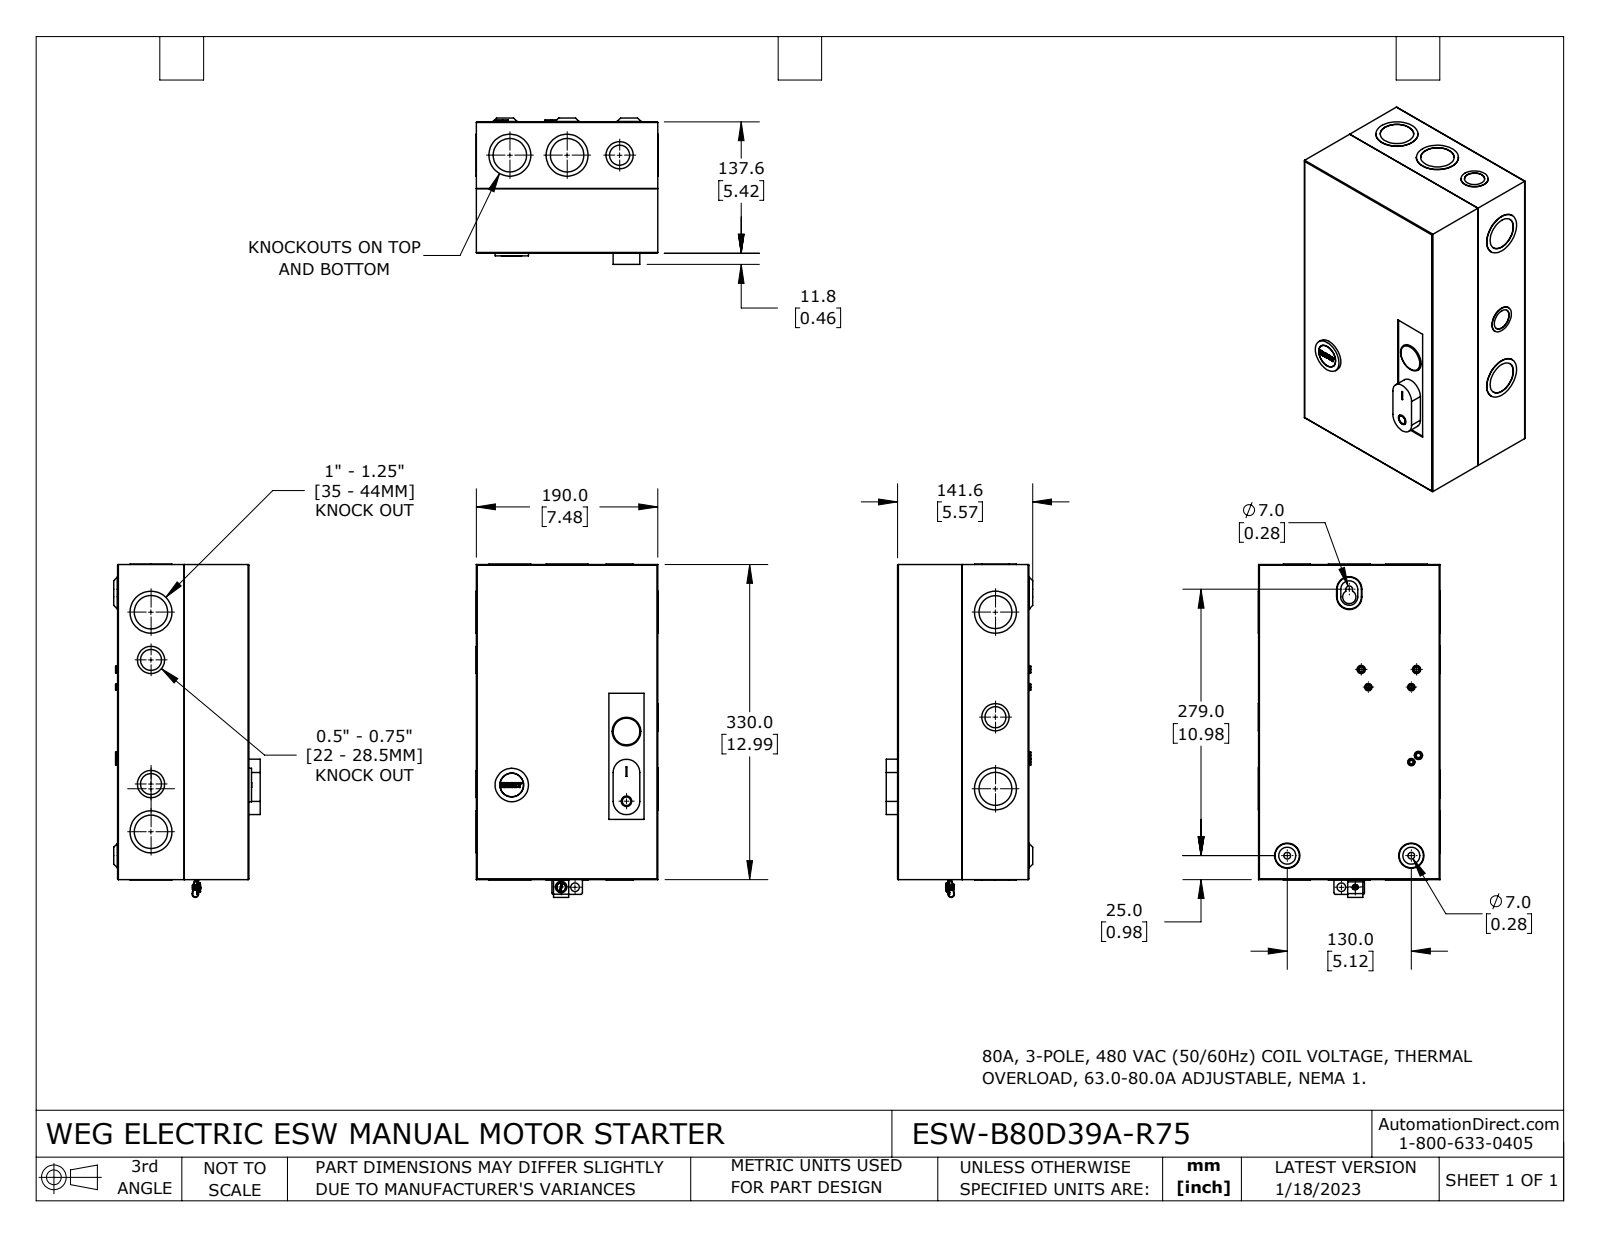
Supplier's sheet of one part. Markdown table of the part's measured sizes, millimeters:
| quantity | value |
| --- | --- |
| part name | ESW-B80D39A-R75 |
| STEP written by | SolidWorks 2021 (CONFIG_CONTROL_DESIGN) |
| units | millimeters |
| bodies | 7 solids, 435 faces (161 planar, 221 cylindrical, 53 other) |
| overall size | 349 × 190.6 × 153.4 |
| volume | 402 800 mm³ |
| surface area | 604 300 mm² |
| round holes (diameter × count) | 35 × 4, 3.7 × 3, 4.6 × 3, 7 × 2, 22 × 2, 22.5 × 2, 34.5 × 2, 6.5 × 1, 7.1 × 1, 9 × 1, 11 × 1, 11.9 × 1 |
| round bosses / shafts (diameter × count) | 44 × 4, 28.5 × 3, 7.1 × 3, 6.1 × 3, 44 × 2, 35 × 1, 30.3 × 1, 29.2 × 1 |
| partial cylindrical surfaces (radius × count) | 0.1 × 34, 0.8 × 8, 2 × 3, 3.5 × 3, 1.5 × 2, 1.9 × 2, 2.7 × 2, 3.1 × 2 |
| main face-to-face distances | 1.2, 136.4, 188.8, 135.2, 137.6, 328.8, 187.6, 190, 1.8, 327.6 |
| hole center spacings | 14.5, 45, 50, 58, 60, 130, 180, 278.7 |
